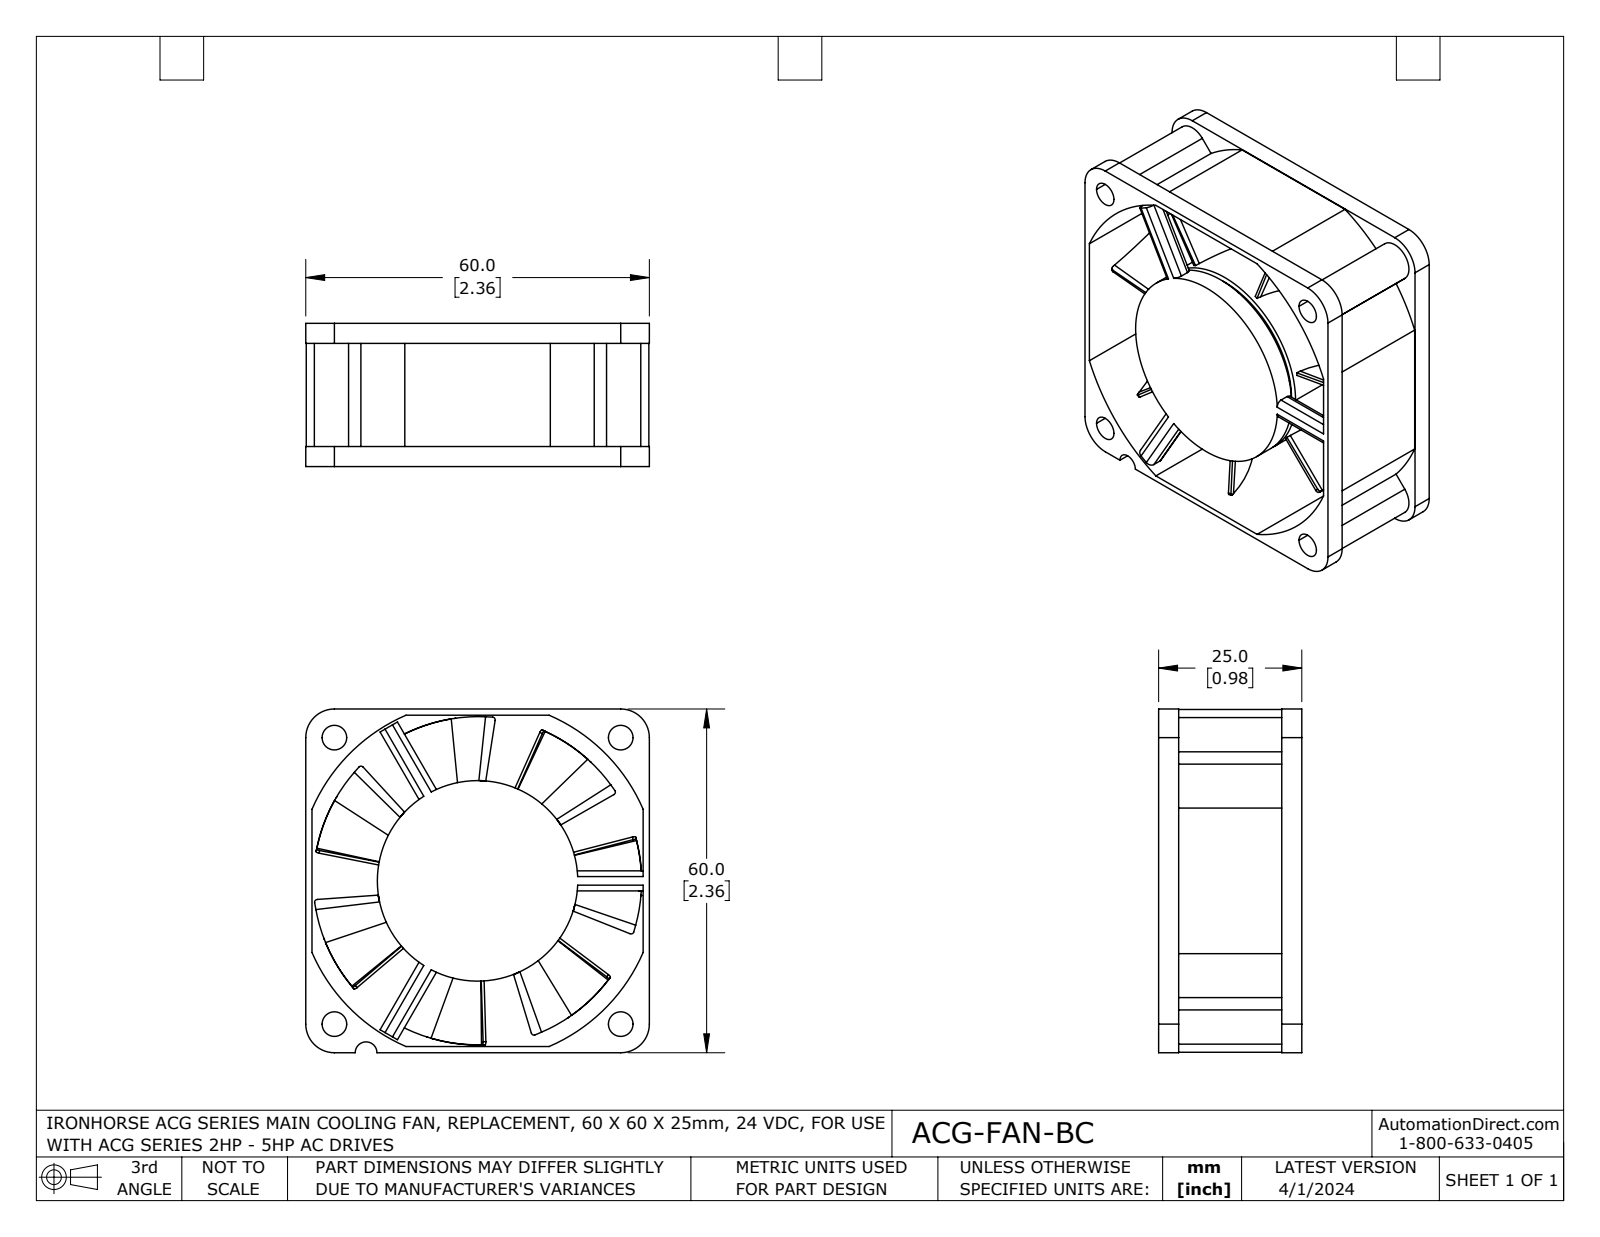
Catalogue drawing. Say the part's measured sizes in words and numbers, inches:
The part is named "ACG-FAN-BC". Its 3-D file was written by "SolidWorks 2021 (AUTOMOTIVE_DESIGN)". It is 2 solids with 228 faces: 58 planar, 58 cylindrical and 112 other. Overall it measures 2.362 by 2.362 by 0.984 inches. Its volume is 0.944 cubic inches and its surface area 42.22 square inches. Round holes: 4 of diameter 0.169, 1 of diameter 1.299. Round bosses or shafts: 1 of diameter 1.378. Partial cylindrical surfaces (rounded edges, fillets, slot ends): 12 of radius 0.039, 4 of radius 0.138, 4 of radius 0.197, 1 of radius 0.075, 1 of radius 1.24, 1 of radius 1.28. The main face-to-face distances are 0.039, 2.316, 0.945, 0.984, 0.043, 2.319, 2.359, 2.276, 0.138, 0.807. The hole center spacings are 1.392, 1.969, 2.784.
